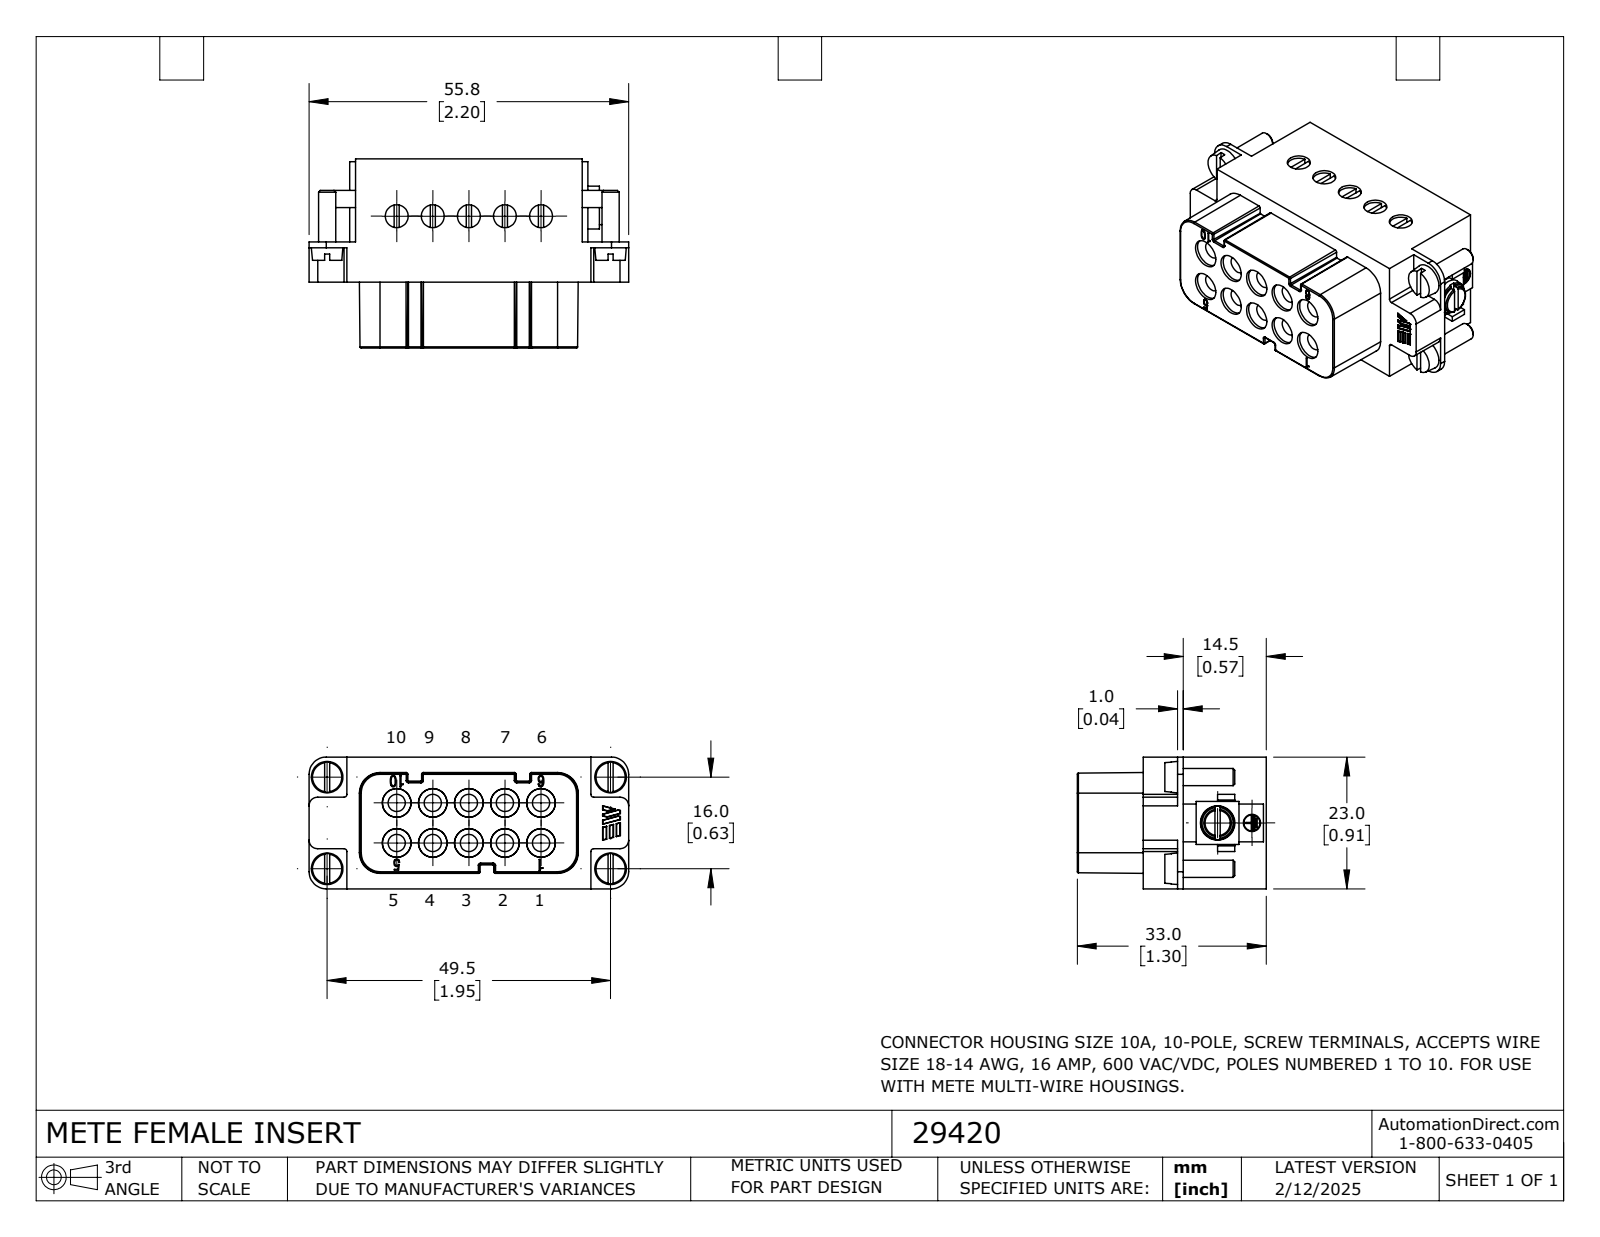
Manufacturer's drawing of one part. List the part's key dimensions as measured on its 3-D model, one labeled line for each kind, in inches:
Part name (STEP PRODUCT): 29420
STEP written by: SolidWorks 2024 (CONFIG_CONTROL_DESIGN)
Units: inches
Bodies: 1 solid, 474 faces (241 planar, 110 cylindrical, 123 other)
Overall size (bounding box): 2.197 × 1.299 × 0.906
Volume: 1.632 in³ · Surface area: 16.48 in²
Round holes (diameter × count): ⌀0.118 ×11, ⌀0.157 ×5
Round bosses / shafts (diameter × count): ⌀0.118 ×4, ⌀0.189 ×1, ⌀0.11 ×1
Partial cylindrical surfaces — rounded edges, fillets, slot ends (radius × count): R0.008 ×12, R0.02 ×4, R0.059 ×4, R0.118 ×4
Main face-to-face distances: 0.906, 0.276, 0.846, 0.453, 1.299, 0.571, 0.728, 0.02, 0.059, 0.039
Hole centre spacings: 0.248, 0.496, 0.371, 0.567, 0.744, 0.276, 0.793, 0.992
